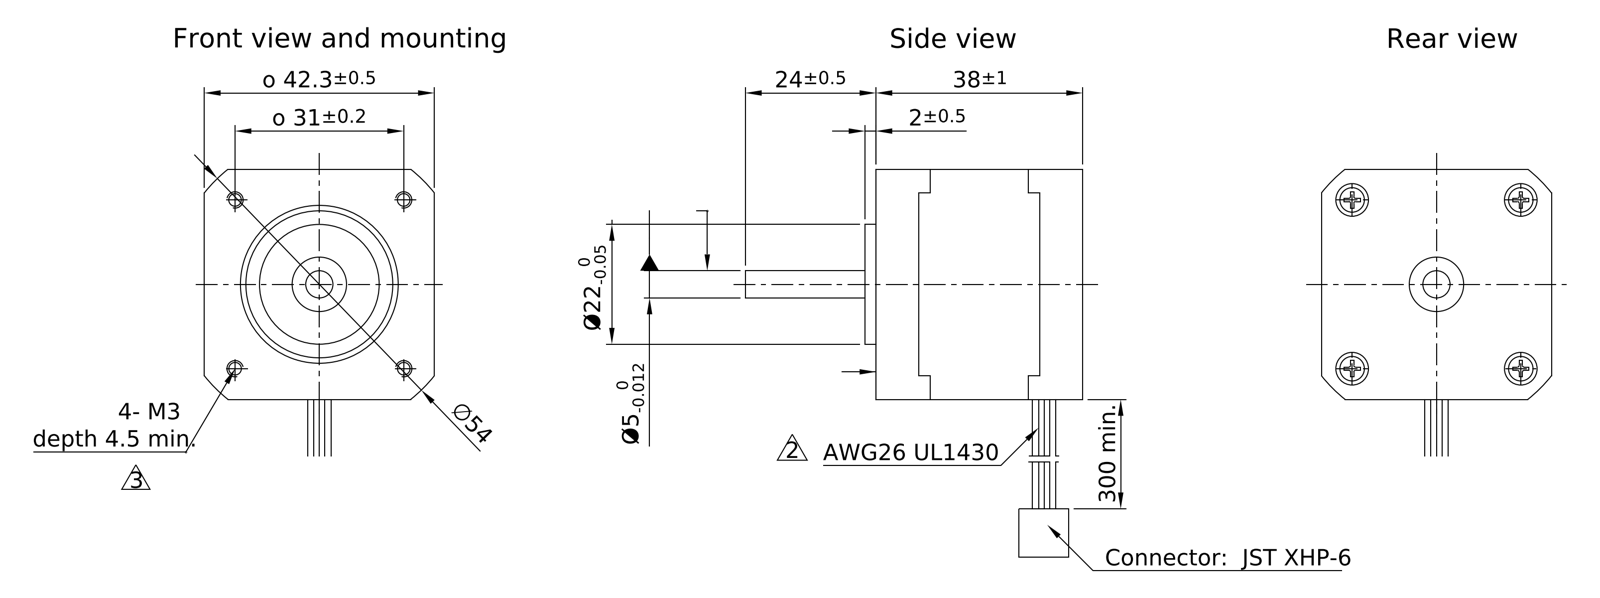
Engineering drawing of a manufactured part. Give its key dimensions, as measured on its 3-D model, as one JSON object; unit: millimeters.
{"part_name": "ST4118M..._A", "step_written_by": "Autodesk Inventor 2010 (AUTOMOTIVE_DESIGN)", "units": "millimeters", "bodies": {"solids": 0, "faces": 157, "planar": 90, "cylindrical": 32, "other": 35}, "overall_size": [62.04, 57, 42], "round_holes": [[6, 4], [2.46, 2], [2.46, 2], [7.5, 1]], "round_bosses_or_shafts": [[1, 4], [22, 1], [5, 1]], "partial_cylinders_radius": [[2, 8], [27, 1]], "face_to_face_distances": [42, 38, 2, 48.08, 40, 11, 27, 37.5, 0.5, 2.5], "hole_center_spacings": [21.92, 31, 43.84]}
